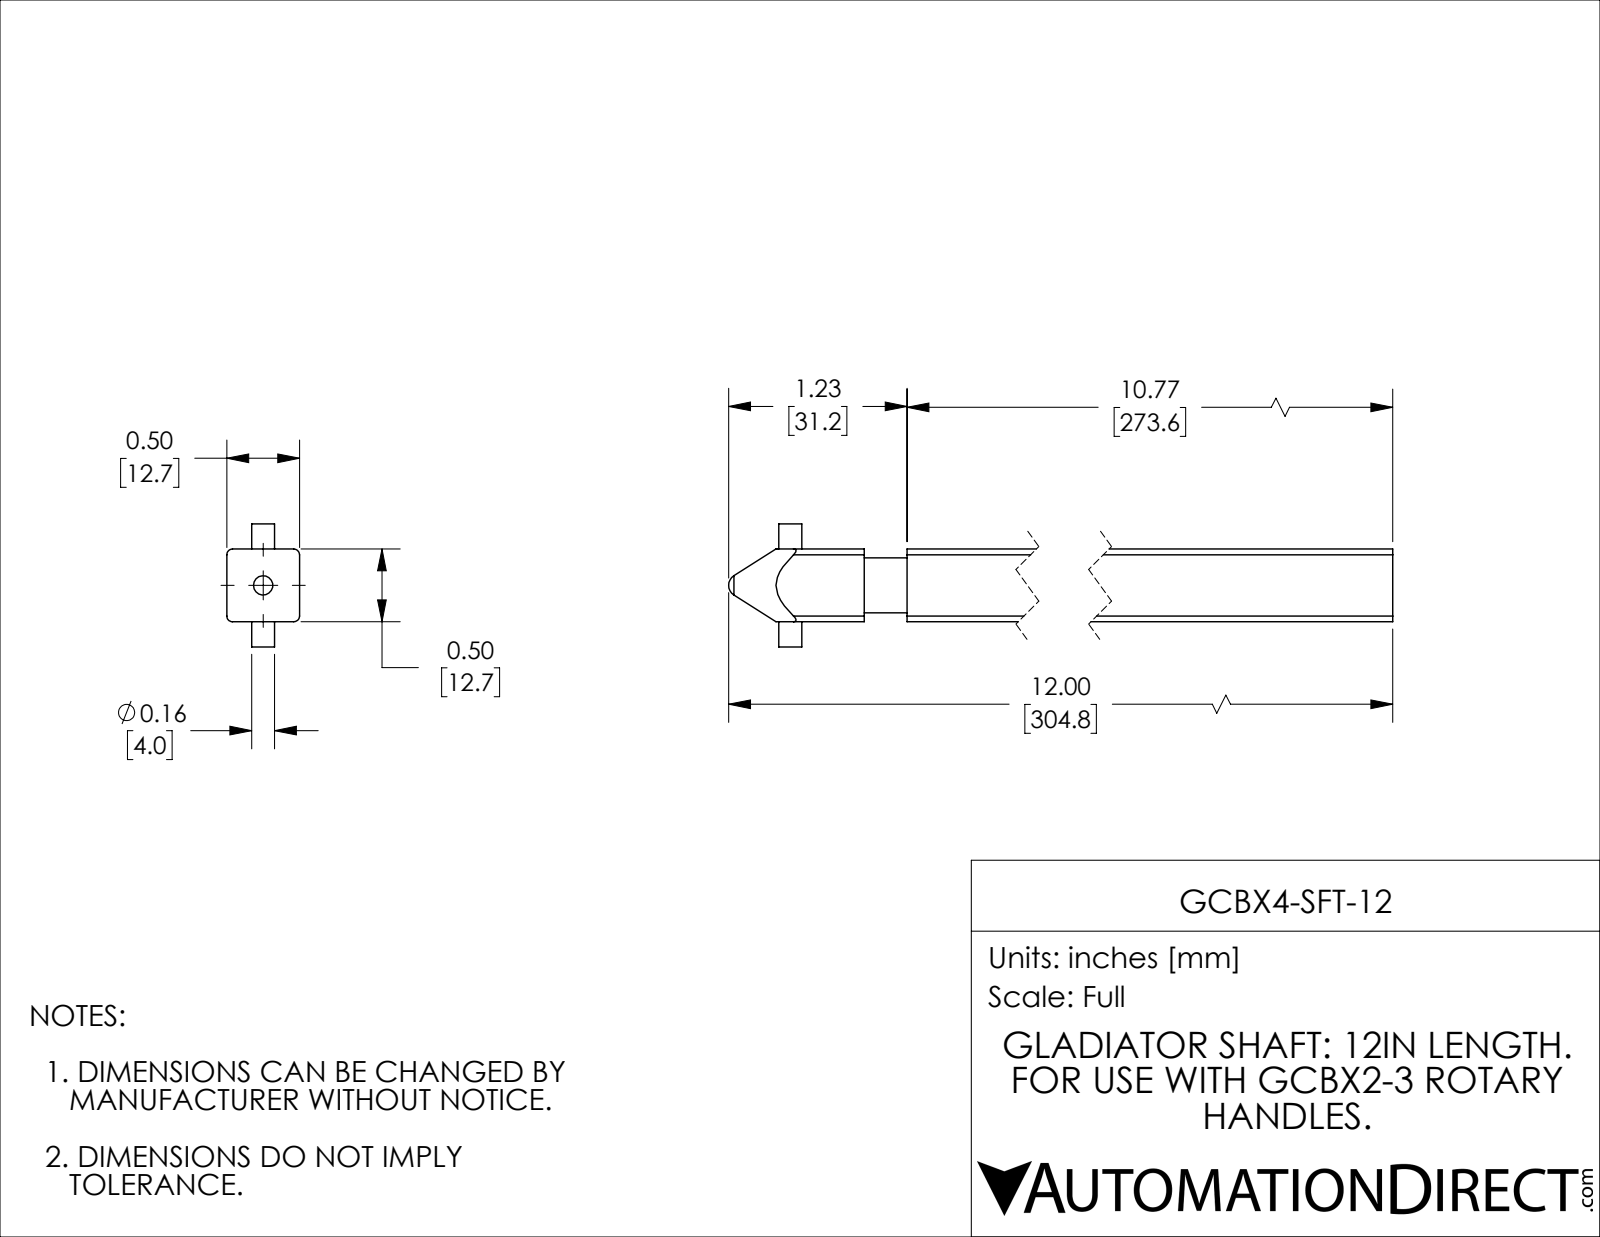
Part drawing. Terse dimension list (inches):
name: GCBX4-SFT-12
written by: SolidWorks 2021 (CONFIG_CONTROL_DESIGN)
unit: in
bodies: 1 solid, 39 faces (15 planar, 17 cylindrical, 7 other)
size: 12 × 0.846 × 0.5
volume: 2.879 in³; area: 23.76 in²
holes: 1× ⌀0.142
bosses: 1× ⌀0.378, 1× ⌀0.157
rounds: 4× R0.039
face distances: 0.5, 10.773, 11.068, 0.295, 0.244, 0.256, 0.173, 0.673, 0.846
